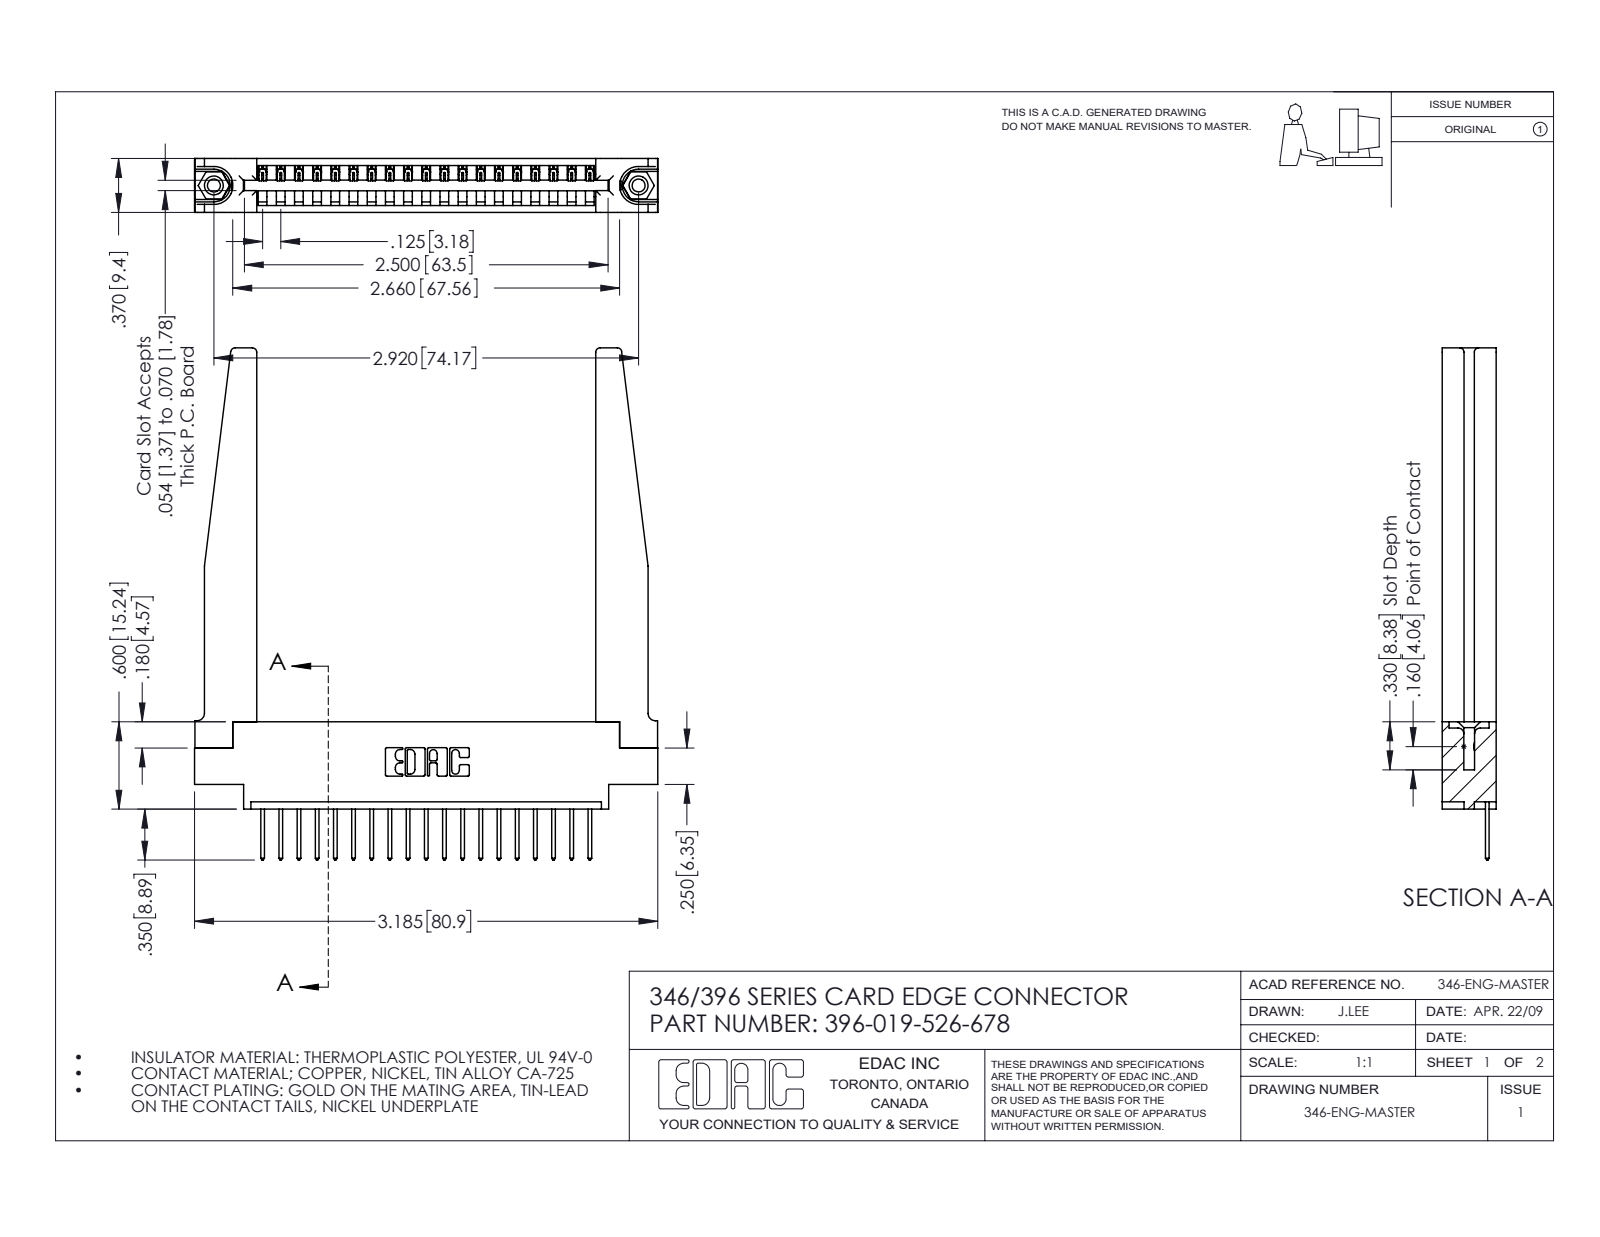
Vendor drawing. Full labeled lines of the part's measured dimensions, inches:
Part name (STEP PRODUCT): 345-250-001_345-250-001-102; 346 Part_0.170 Offset - 0.156 Dia-TH; 346-220-078_345-220-078; 396-019-526-678 (+1 more)
STEP written by: SolidWorks 2016 (CONFIG_CONTROL_DESIGN)
Units: inches
Bodies: 24 solids, 1462 faces (982 planar, 428 cylindrical, 52 other)
Overall size (bounding box): 3.52 × 3.185 × 0.37
Volume: 0.874 in³ · Surface area: 24.34 in²
Round holes (diameter × count): ⌀0.089 ×2, ⌀0.125 ×2, ⌀0.156 ×2, ⌀0.064 ×1
Round bosses / shafts (diameter × count): ⌀0.155 ×2
Partial cylindrical surfaces — rounded edges, fillets, slot ends (radius × count): R0.006 ×38, R0.01 ×38, R0.01 ×22, R0.03 ×8, R0.007 ×6, R0.031 ×6, R0.026 ×3, R0.031 ×2
Main face-to-face distances: 0.37, 0.072, 0.048, 0.322, 0.15, 0.148, 0.25, 0.298, 0.025, 0.102
Hole centre spacings: 0.246, 2.713, 2.92
